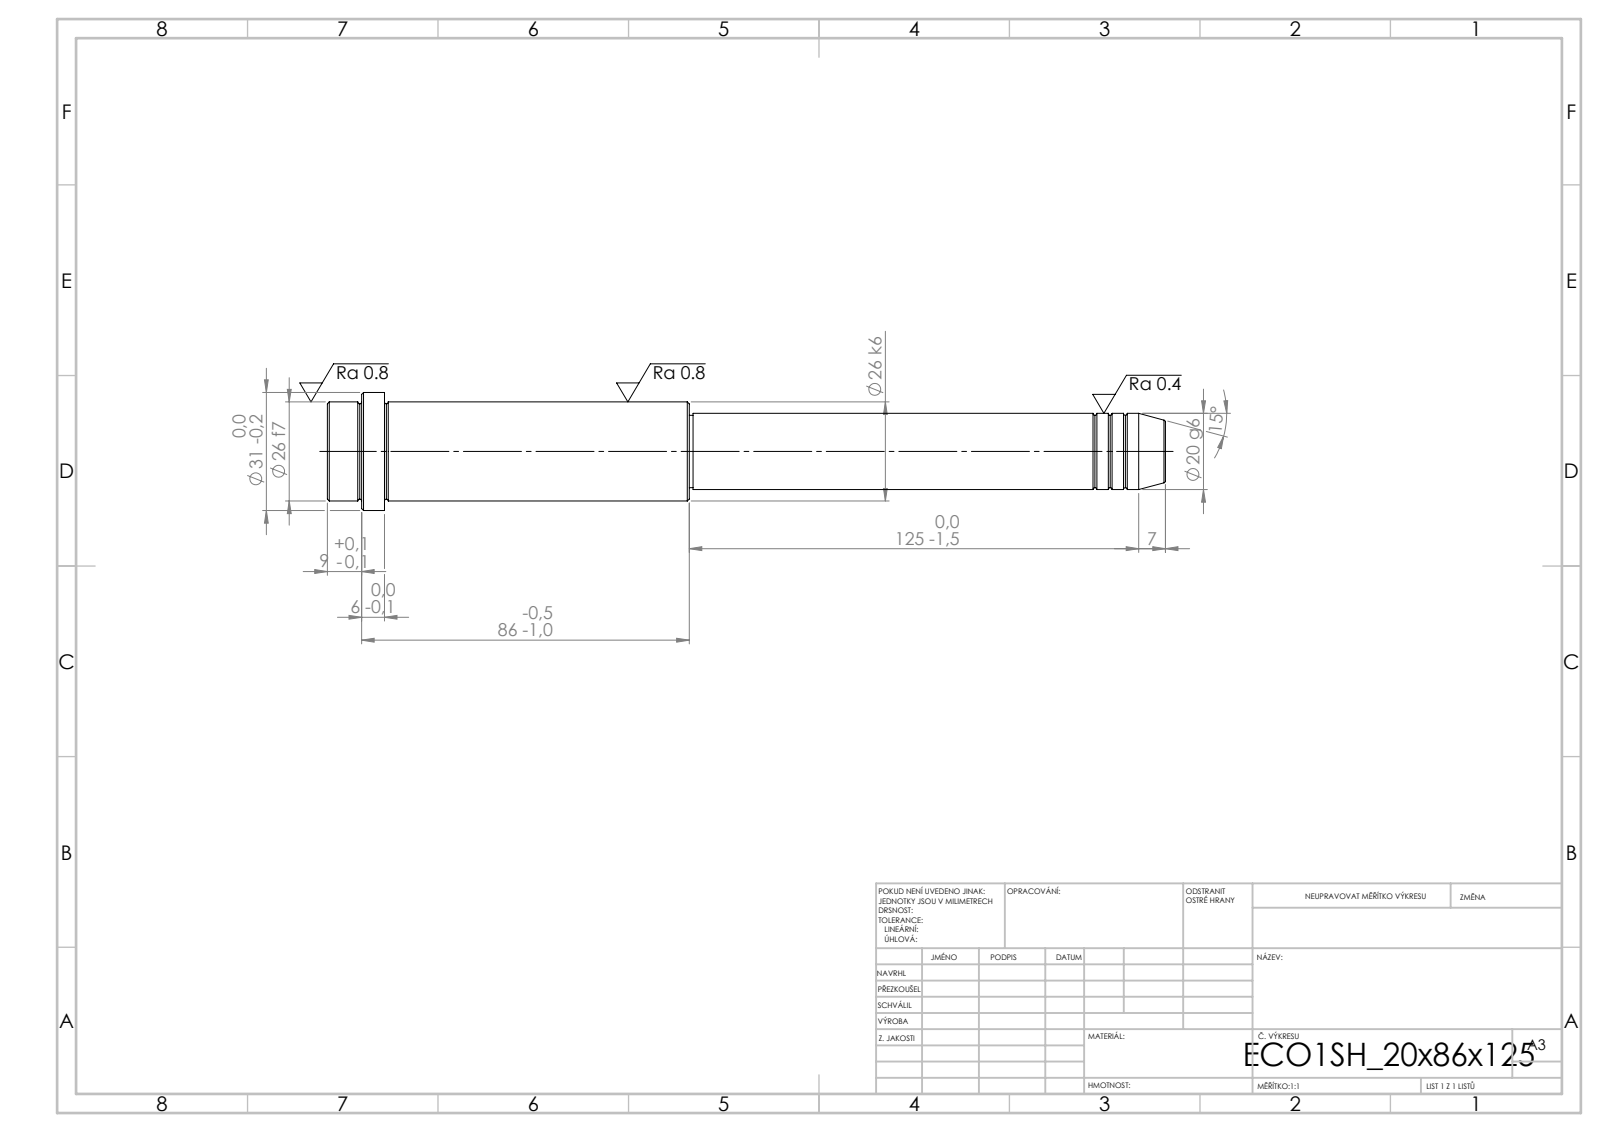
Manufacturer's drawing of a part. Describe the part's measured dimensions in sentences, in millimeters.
Its 3-D file was written by "SolidWorks 2019 (CONFIG_CONTROL_DESIGN)". It is 1 solid with 52 faces: 6 planar, 16 cylindrical and 30 other. Overall it measures 220 by 31 by 31 millimeters. Its volume is 90 465 cubic millimeters and its surface area 17 244 square millimeters. Round bosses or shafts: 1 of diameter 31, 1 of diameter 26, 1 of diameter 20, 1 of diameter 19. The main face-to-face distances are 15, 80, 95, 125, 205, 220, 211, 86, 6, 9.
